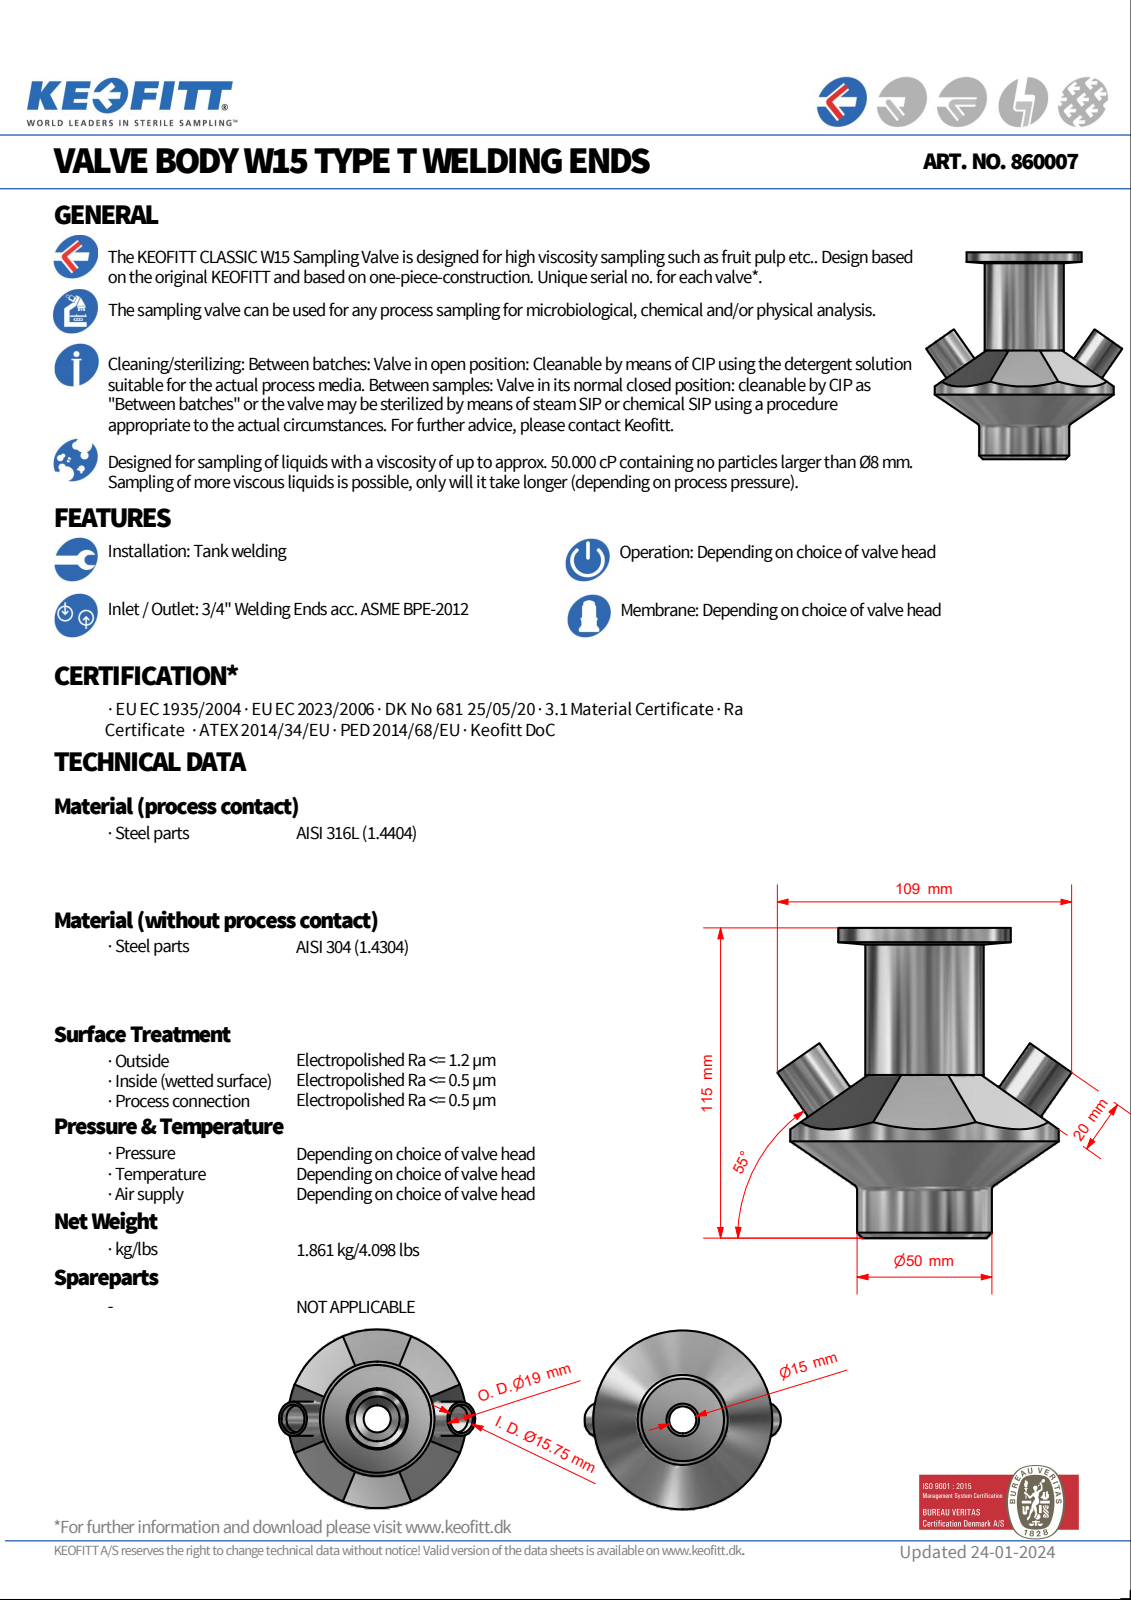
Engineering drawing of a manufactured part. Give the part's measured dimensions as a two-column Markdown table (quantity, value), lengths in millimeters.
| quantity | value |
| --- | --- |
| part name | 860007 |
| STEP written by | Autodesk Inventor 2020 (AUTOMOTIVE_DESIGN) |
| units | millimeters |
| bodies | 1 solid, 58 faces (24 planar, 15 cylindrical, 19 other) |
| overall size | 115.2 × 109.27 × 99.5 |
| volume | 314 059 mm³ |
| surface area | 42 546 mm² |
| round holes (diameter × count) | 15 × 3, 34 × 1, 39 × 1, 60 × 1 |
| round bosses / shafts (diameter × count) | 19 × 2, 99.5 × 1, 64 × 1, 50 × 1, 44 × 1, 38 × 1 |
| partial cylindrical surfaces (radius × count) | 18.54 × 1 |
| main face-to-face distances | 113.2, 109.9, 3.3, 115.2, 5.3, 2, 20, 1.57, 108.33, 111.63 |
